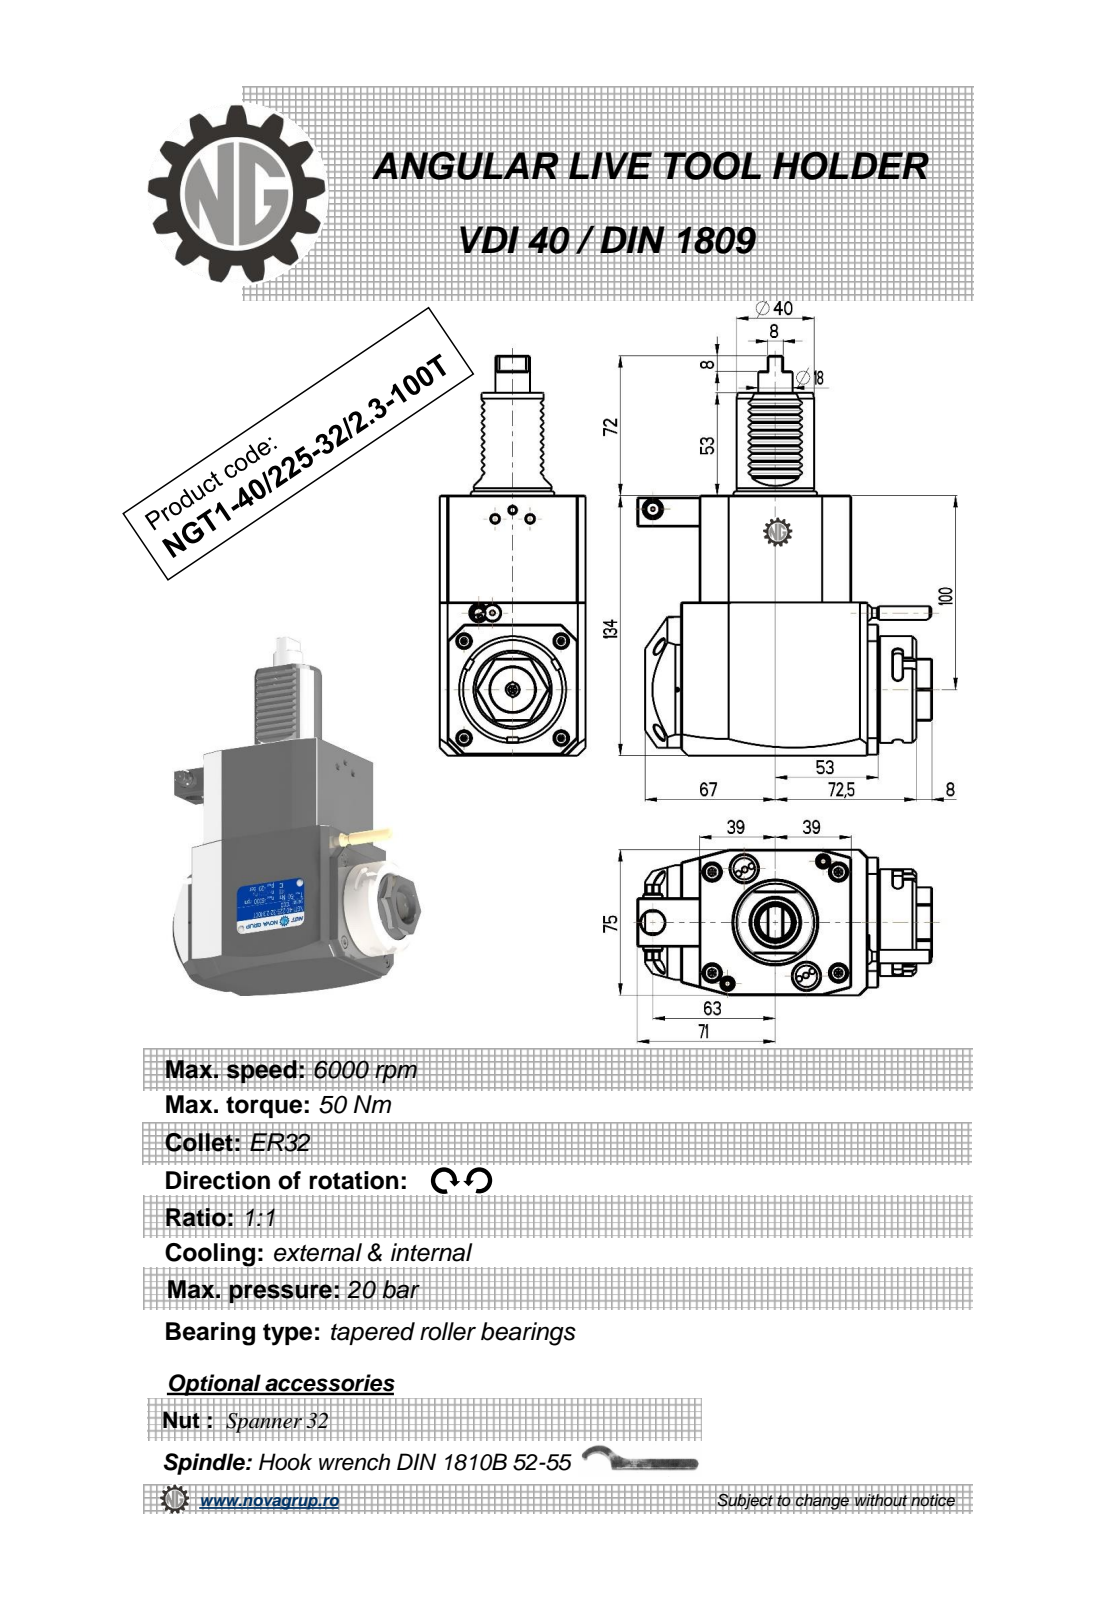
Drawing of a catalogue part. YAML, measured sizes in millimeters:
part_name: "NGT1_40_225_32_1_3_100T"
step_written_by: "PRO/ENGINEER BY PARAMETRIC TECHNOLOGY CORPORATION, 2010280 (CONFIG_CONTROL_DESIGN)"
units: millimeters
bodies: {solids: 1, faces: 388, planar: 223, cylindrical: 89, other: 76}
overall_size: [206, 151.5, 75]
volume: 1066000
surface_area: 77483
round_holes:
  - {diameter: 2, count: 1}
  - {diameter: 2.5, count: 1}
  - {diameter: 3, count: 1}
  - {diameter: 9.5, count: 1}
  - {diameter: 12, count: 1}
  - {diameter: 23, count: 1}
round_bosses_or_shafts:
  - {diameter: 8, count: 2}
  - {diameter: 55, count: 1}
  - {diameter: 48, count: 1}
  - {diameter: 40, count: 1}
  - {diameter: 17.8, count: 1}
  - {diameter: 10, count: 1}
  - {diameter: 7, count: 1}
  - {diameter: 5, count: 1}
partial_cylinders:
  - {radius: 0.3, count: 20}
  - {radius: 2.5, count: 6}
  - {radius: 0.8, count: 2}
  - {radius: 180, count: 2}
  - {radius: 3.85, count: 1}
  - {radius: 4.25, count: 1}
  - {radius: 24.5, count: 1}
  - {radius: 37.5, count: 1}
face_to_face_distances: [75, 134, 78, 14, 92, 25, 84.88, 54, 111.5, 33.5]
hole_center_spacings: [43.2, 55.81, 92.5]
